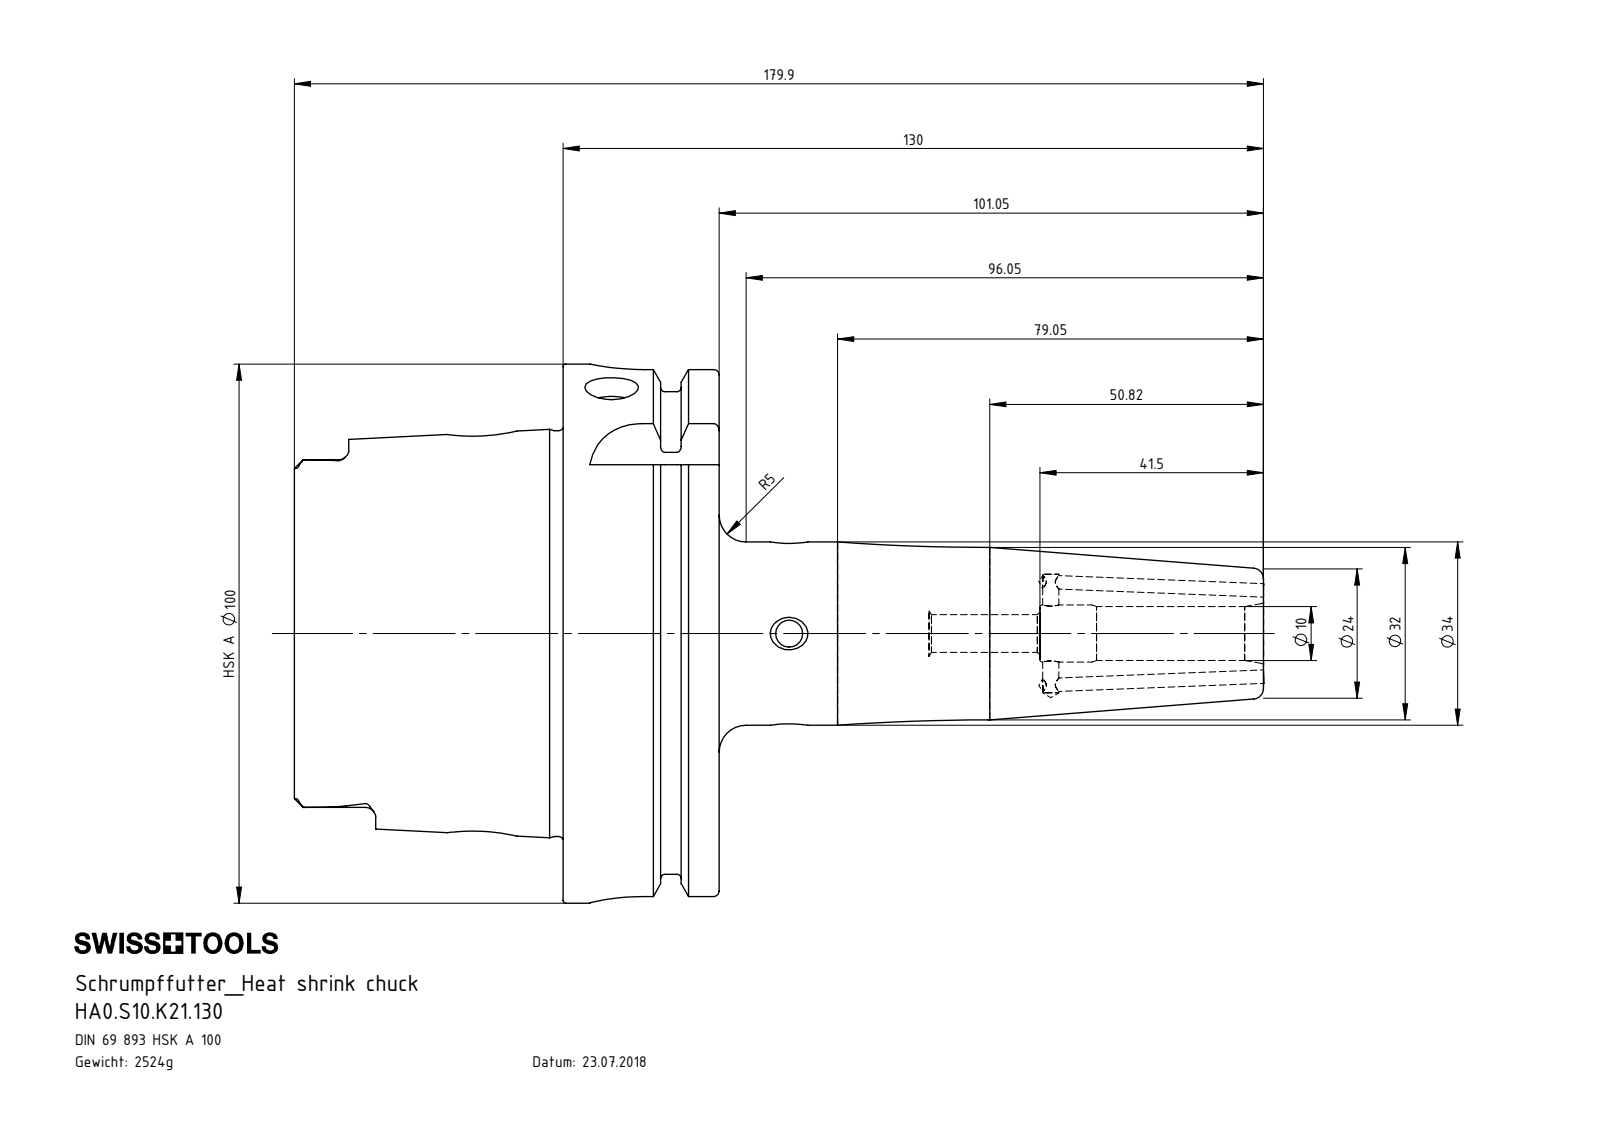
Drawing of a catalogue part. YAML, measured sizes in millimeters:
part_name: "HA0-S10.K21.130; ERU-CJ2.001.006; ERU-AN3.K01.020_A; HA0-S10.K21.130_C_Fertigbearbeitung"
step_written_by: "SolidWorks 2012 (CONFIG_CONTROL_DESIGN)"
units: millimeters
bodies: {solids: 4, faces: 298, planar: 95, cylindrical: 88, other: 115}
overall_size: [179.98, 100, 100]
volume: 321585
surface_area: 63886
round_holes:
  - {diameter: 10, count: 4}
  - {diameter: 2.5, count: 2}
  - {diameter: 5, count: 2}
  - {diameter: 3, count: 1}
  - {diameter: 4, count: 1}
  - {diameter: 7, count: 1}
  - {diameter: 8.5, count: 1}
  - {diameter: 10.6, count: 1}
  - {diameter: 12, count: 1}
  - {diameter: 22.5, count: 1}
  - {diameter: 26, count: 1}
  - {diameter: 53, count: 1}
round_bosses_or_shafts:
  - {diameter: 3, count: 2}
  - {diameter: 100, count: 1}
  - {diameter: 91.95, count: 1}
  - {diameter: 75.26, count: 1}
  - {diameter: 34, count: 1}
  - {diameter: 32, count: 1}
  - {diameter: 8, count: 1}
partial_cylinders:
  - {radius: 1.9, count: 6}
  - {radius: 4.88, count: 4}
  - {radius: 10, count: 4}
face_to_face_distances: [28.95, 16.5, 12.45, 49.9, 62.35, 78.85, 78.2, 28.3, 15.85, 0.65]
hole_center_spacings: [34.95, 48.55, 56.95, 105.5]
